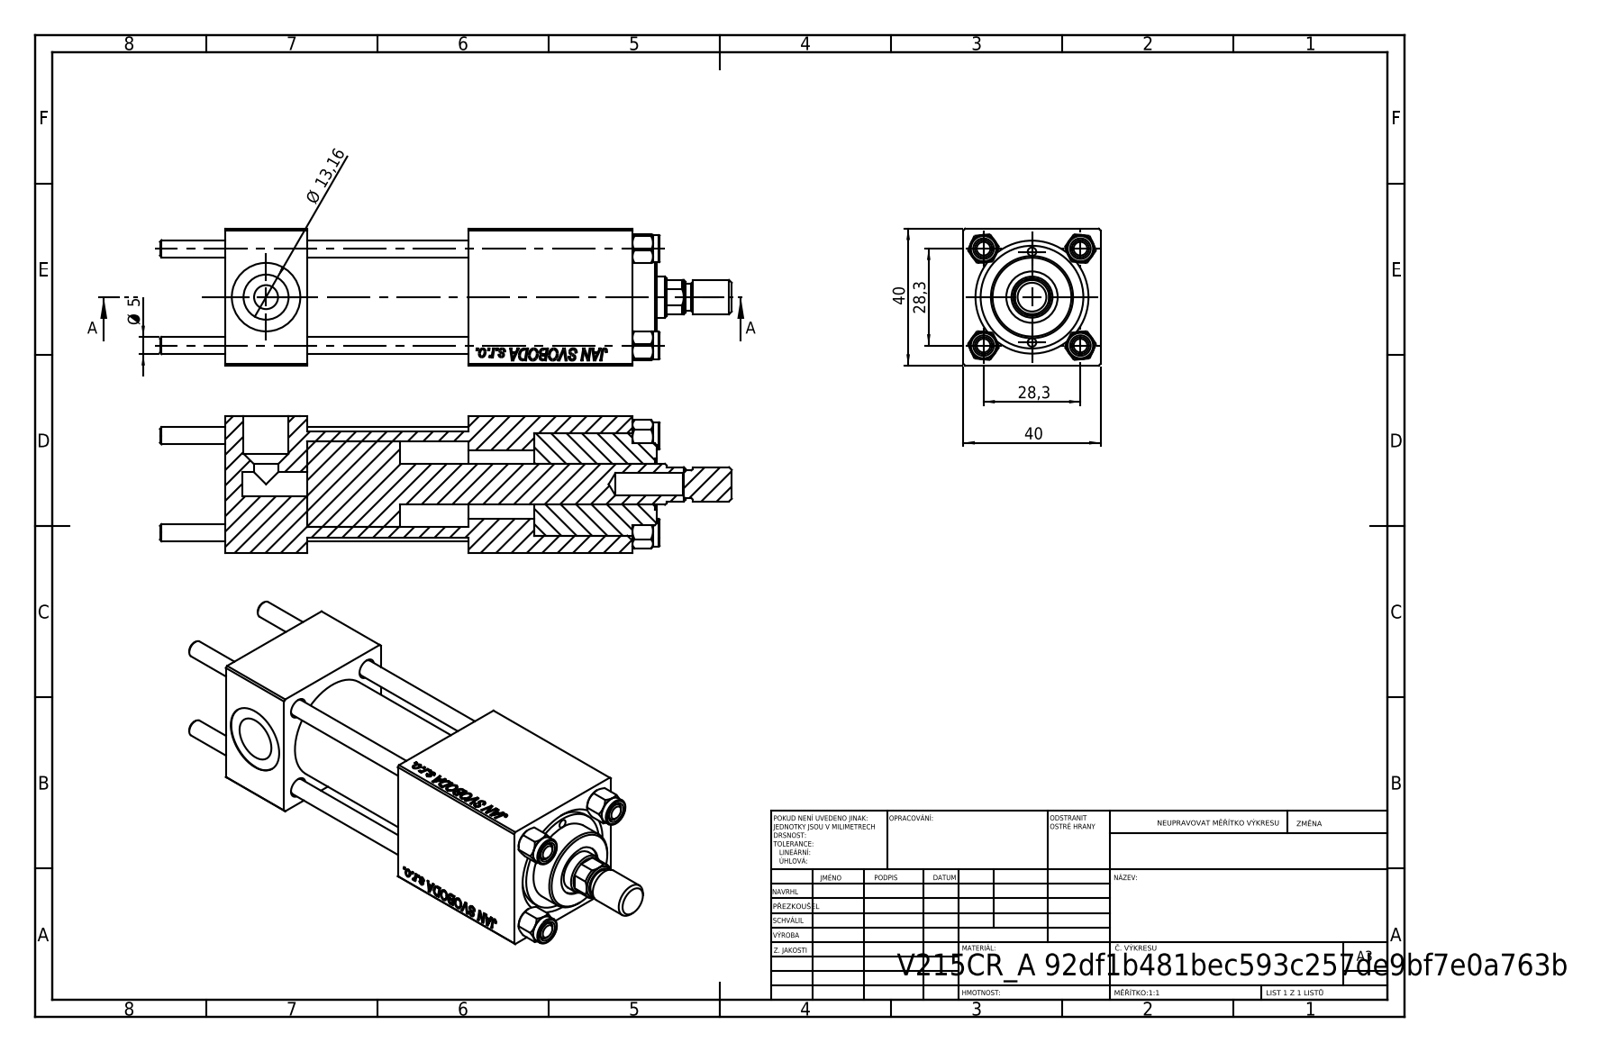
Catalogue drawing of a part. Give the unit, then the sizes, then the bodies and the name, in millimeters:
Units: millimetres
Overall size (bounding box): 167 × 40 × 40
Round holes (diameter × count): ⌀5 ×4, ⌀20 ×3, ⌀2.5 ×2, ⌀7 ×2, ⌀13.16 ×2, ⌀6.5 ×1, ⌀12 ×1, ⌀15 ×1, ⌀25 ×1, ⌀30 ×1
Round bosses / shafts (diameter × count): ⌀8 ×5, ⌀31 ×1, ⌀24 ×1, ⌀10 ×1
Partial cylindrical surfaces — rounded edges, fillets, slot ends (radius × count): R5.5 ×1
Main face-to-face distances: 40, 24, 90.3, 66.3, 119, 95, 28.7, 71, 47, 19.3
Hole centre spacings: 14.18, 20.01, 28.3, 30.84, 13.25, 40.02, 26.5
Volume: 145 725 mm³ · Surface area: 59 562 mm²
Bodies: 12 solids, 1152 faces (523 planar, 87 cylindrical, 542 other)
Part name (STEP PRODUCT): V215CR_BODY_A; ROD_END_AH; NUT_M5; V215CR_VCP (+2 more)
STEP written by: SolidWorks 2019 (CONFIG_CONTROL_DESIGN)
